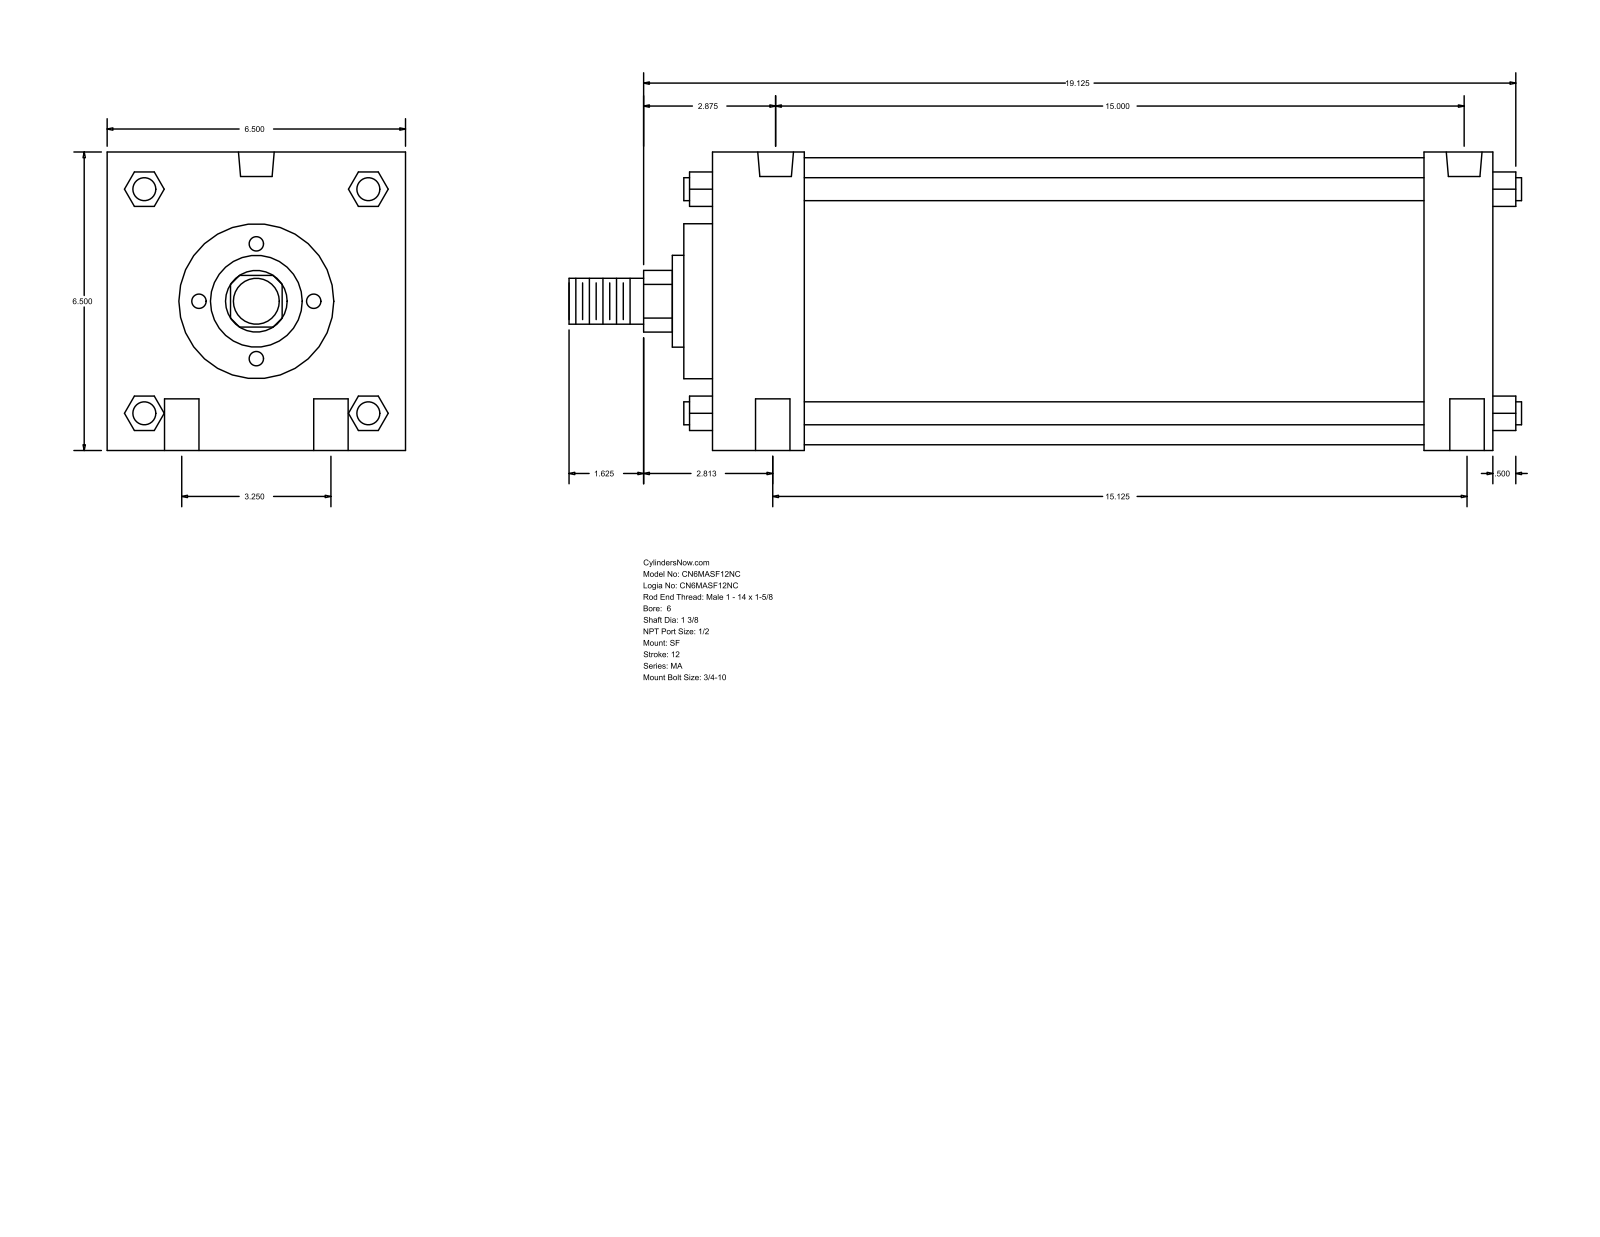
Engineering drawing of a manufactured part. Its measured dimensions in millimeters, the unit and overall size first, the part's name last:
Units: millimetres
Overall size (bounding box): 527.05 × 165.1 × 165.1
Round holes (diameter × count): ⌀19.05 ×4, ⌀17.46 ×2, ⌀19.77 ×2
Round bosses / shafts (diameter × count): ⌀12.7 ×4, ⌀158.75 ×1, ⌀85.72 ×1, ⌀50.8 ×1, ⌀34.92 ×1, ⌀25.4 ×1
Partial cylindrical surfaces — rounded edges, fillets, slot ends (radius × count): R17.06 ×1
Main face-to-face distances: 165.1, 431.8, 393.7, 50.8, 38.1, 342.9, 381, 66.67, 15.87, 447.67
Hole centre spacings: 41.3, 384.8, 82.54, 384.17, 392.94, 380.99, 381
Bodies: 0 solids, 126 faces (95 planar, 31 cylindrical, 0 other)
Part name (STEP PRODUCT): MA_SF__0600_1.375
STEP written by: GSSL Pune (CONFIG_CONTROL_DESIGN)
